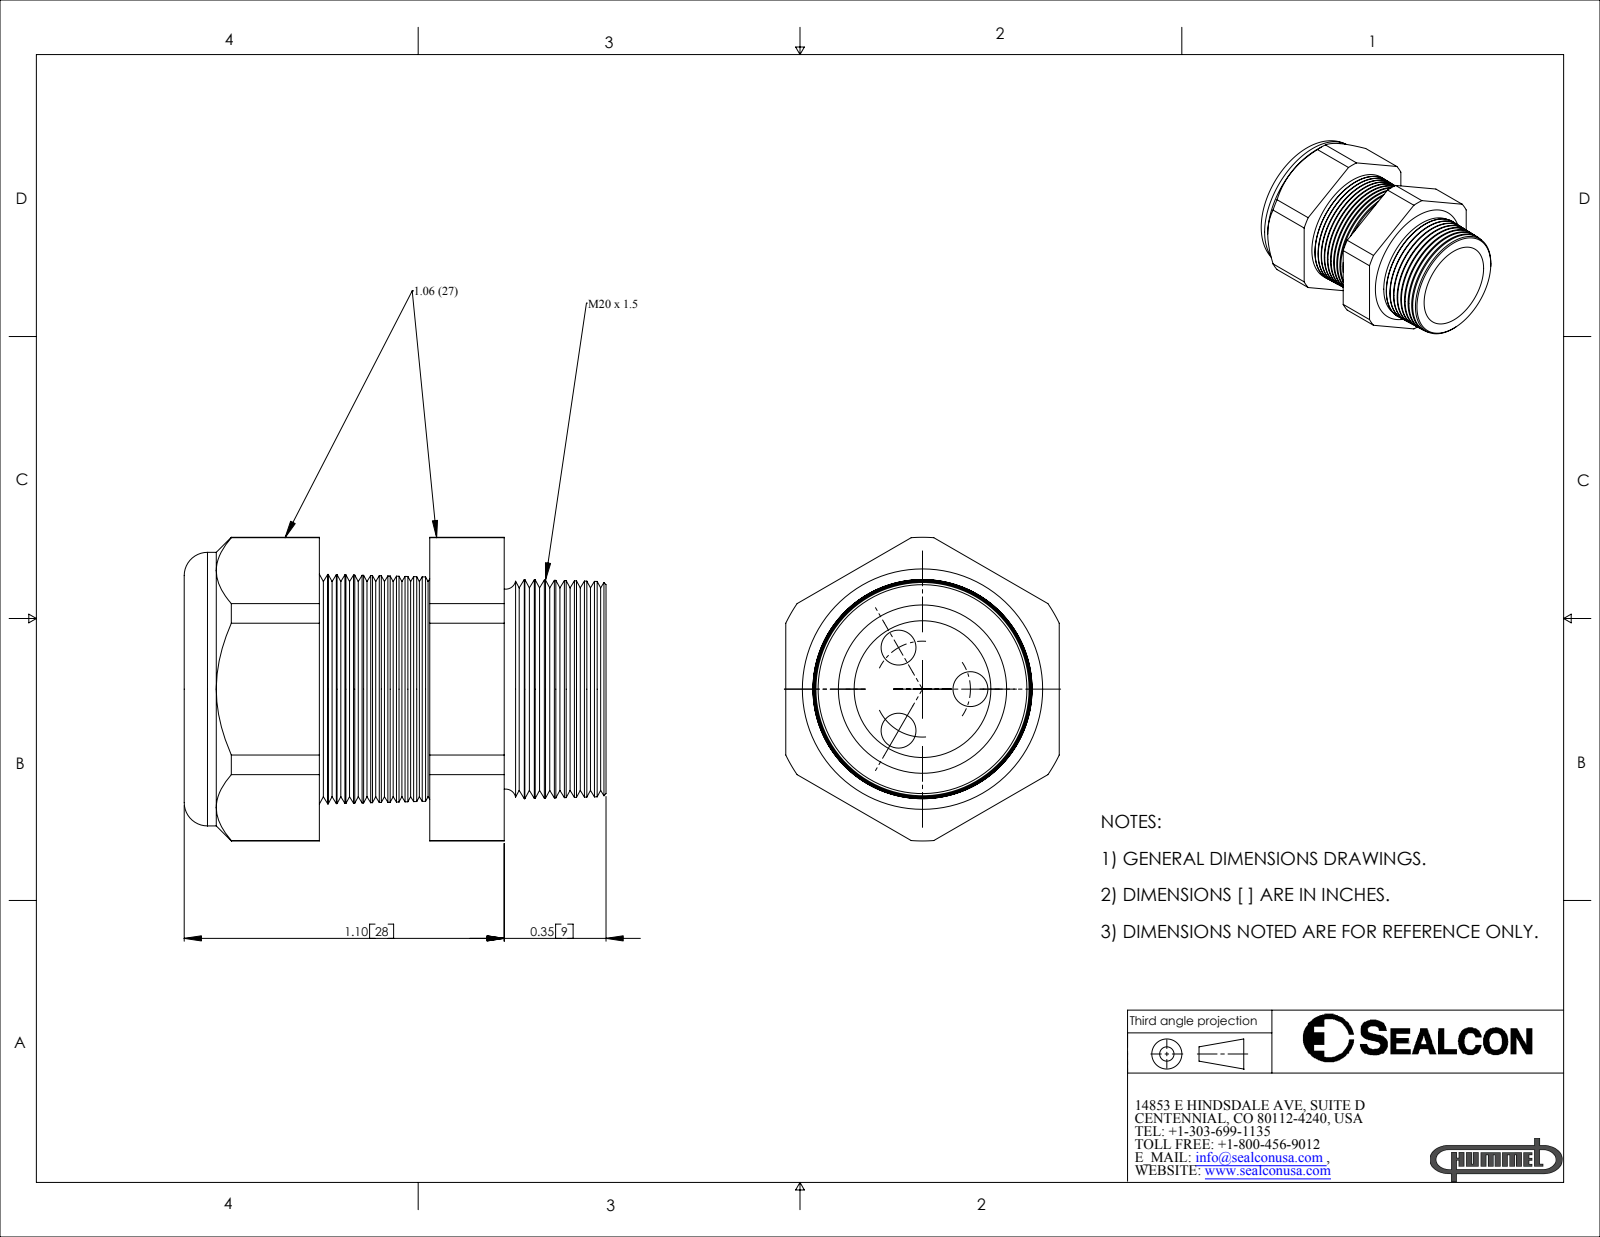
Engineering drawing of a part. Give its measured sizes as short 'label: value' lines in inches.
name: CD22M1-GY
written by: SolidWorks 2007 (CONFIG_CONTROL_DESIGN)
unit: in
bodies: 2 solids, 192 faces (20 planar, 26 cylindrical, 146 other)
size: 1.45 × 1.043 × 0.94
volume: 0.587 in³; area: 10.21 in²
holes: 3× ⌀0.12, 1× ⌀0.45, 1× ⌀0.47
bosses: 1× ⌀0.94
rounds: 1× R0.522
face distances: 0.94, 0.844, 0.465, 0.38, 1.1, 0.635, 0.256, 1.45, 0.985, 0.606
hole spacings: 0.165, 0.285
